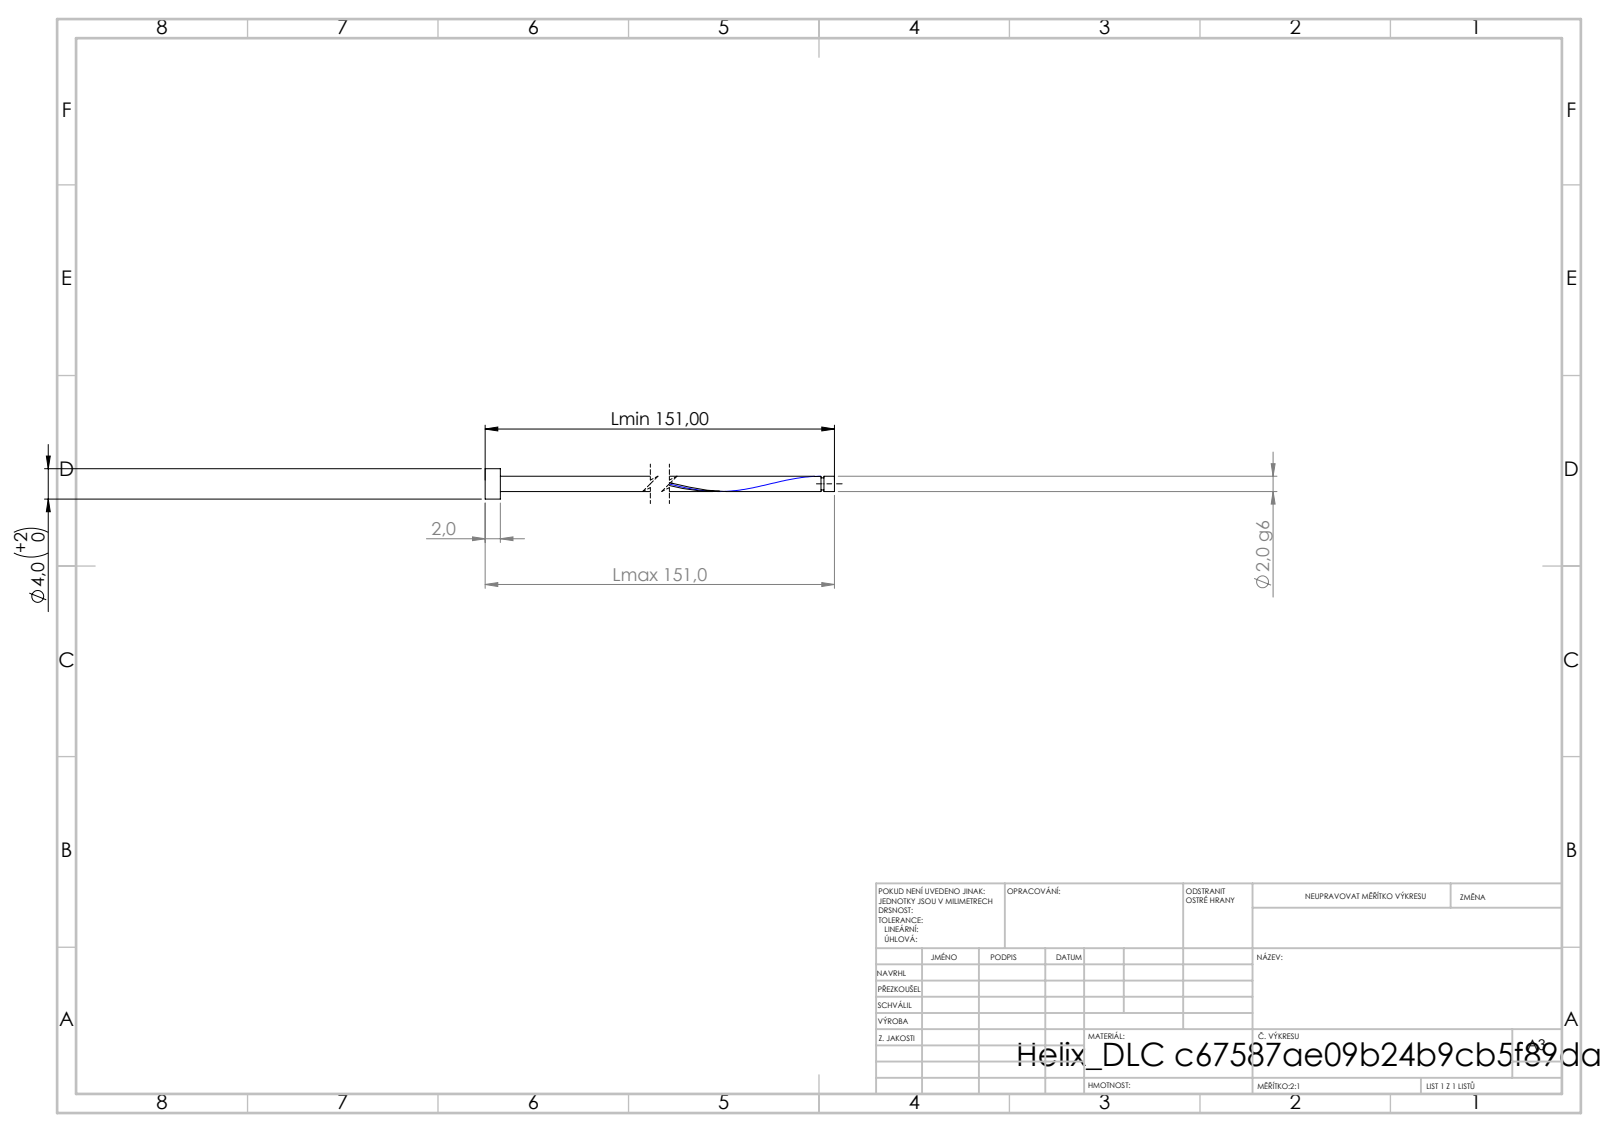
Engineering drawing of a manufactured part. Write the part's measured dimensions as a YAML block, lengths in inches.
step_written_by: "SolidWorks 2019 (CONFIG_CONTROL_DESIGN)"
units: inches
bodies: {solids: 1, faces: 16, planar: 6, cylindrical: 9, other: 1}
overall_size: [5.945, 0.157, 0.157]
volume: 0.037
surface_area: 2.075
round_bosses_or_shafts:
  - {diameter: 0.157, count: 1}
  - {diameter: 0.079, count: 1}
  - {diameter: 0.063, count: 1}
face_to_face_distances: [0.079, 5.945, 5.866, 5.891, 5.812, 0.054, 5.875, 5.796, 0.016, 0.07]
